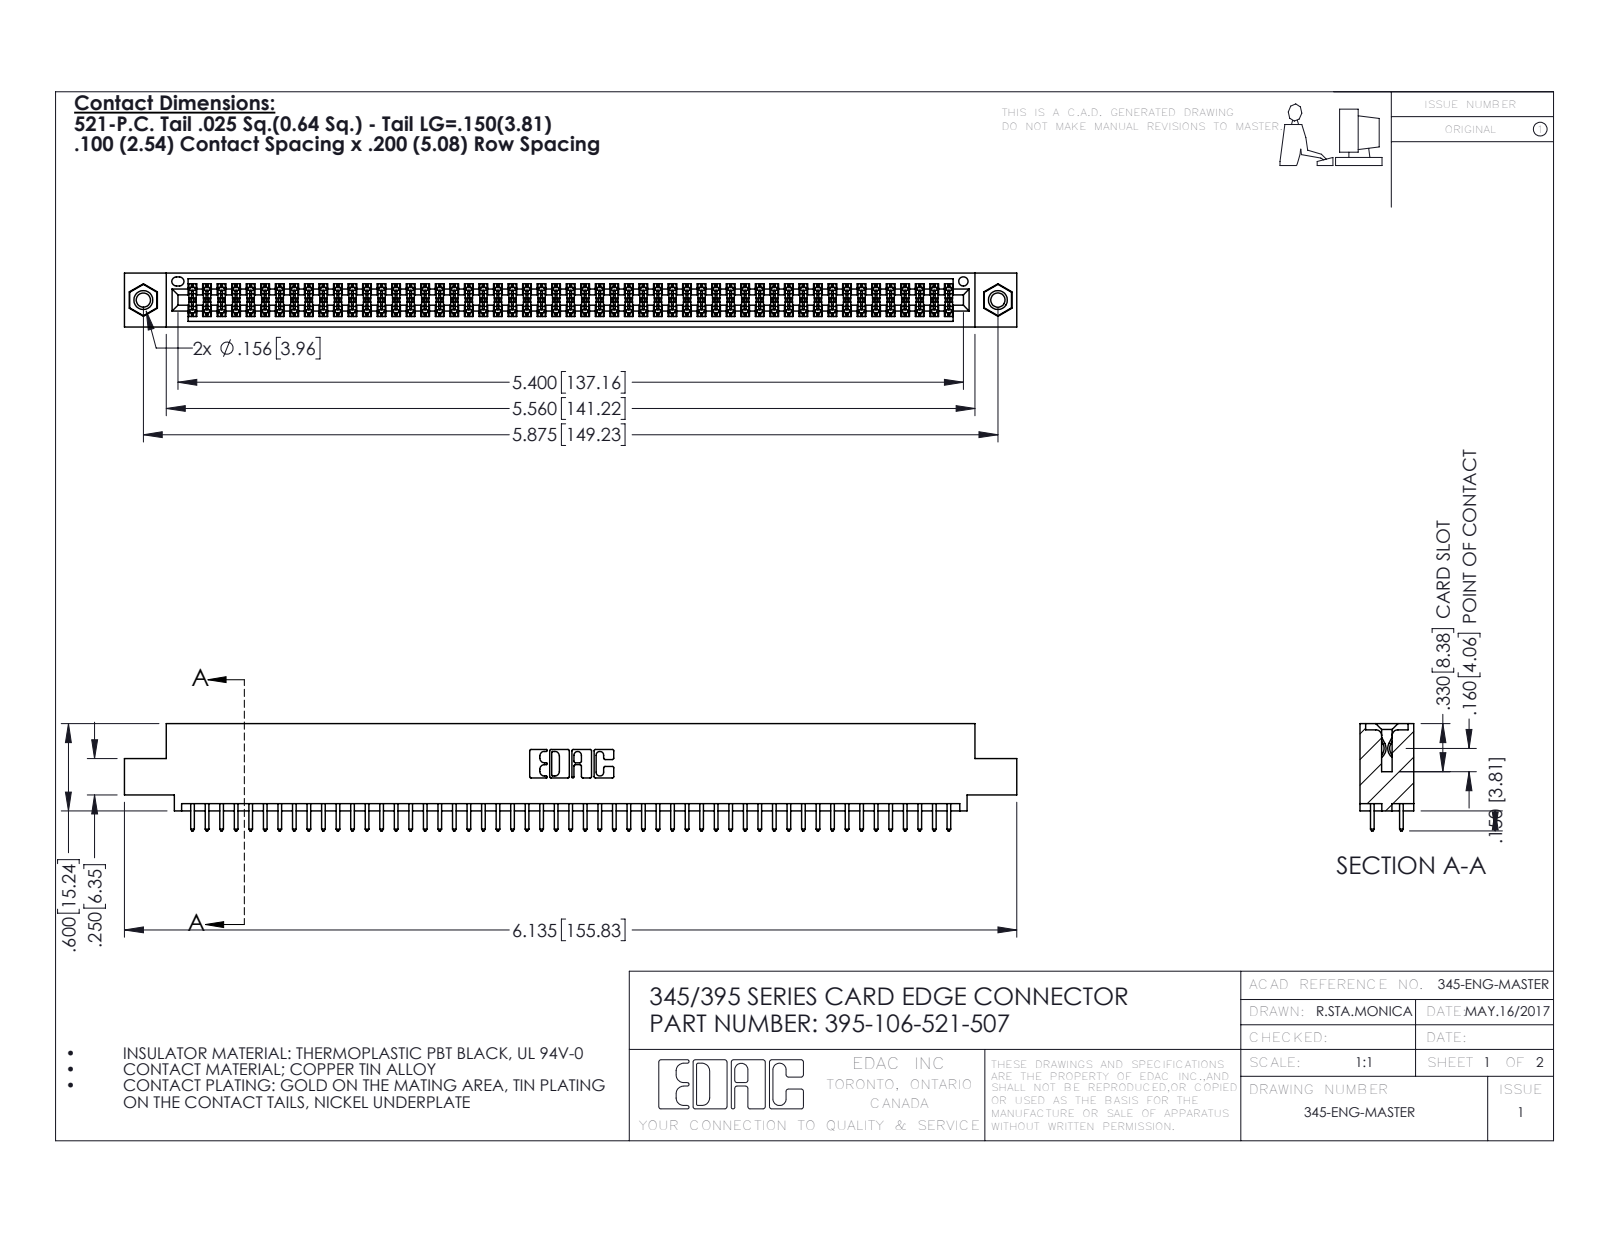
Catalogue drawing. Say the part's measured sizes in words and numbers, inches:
The part is named "345-292-001_345-293-121; 345 Part_0.110 Offset - 0.156 Dia-TI; 345-250-001_345-250-005-103; 395-106-521-507". Its 3-D file was written by "SolidWorks 2016 (CONFIG_CONTROL_DESIGN)". It is 109 solids with 5490 faces: 3614 planar, 1860 cylindrical and 16 other. Overall it measures 6.135 by 0.737 by 0.37 inches. Its volume is 0.922 cubic inches and its surface area 34.7 square inches. Round holes: 2 of diameter 0.098, 2 of diameter 0.125, 2 of diameter 0.156, 1 of diameter 0.064. Round bosses or shafts: 2 of diameter 0.155. Partial cylindrical surfaces (rounded edges, fillets, slot ends): 159 of radius 0.006, 106 of radius 0.01, 22 of radius 0.01, 6 of radius 0.007, 6 of radius 0.031, 3 of radius 0.026, 2 of radius 0.014, 2 of radius 0.019. The main face-to-face distances are 0.072, 0.298, 0.2, 0.098, 0.272, 0.025, 0.37, 0.225, 0.175, 0.149. The hole center spacings are 0.27, 5.639, 5.875.
